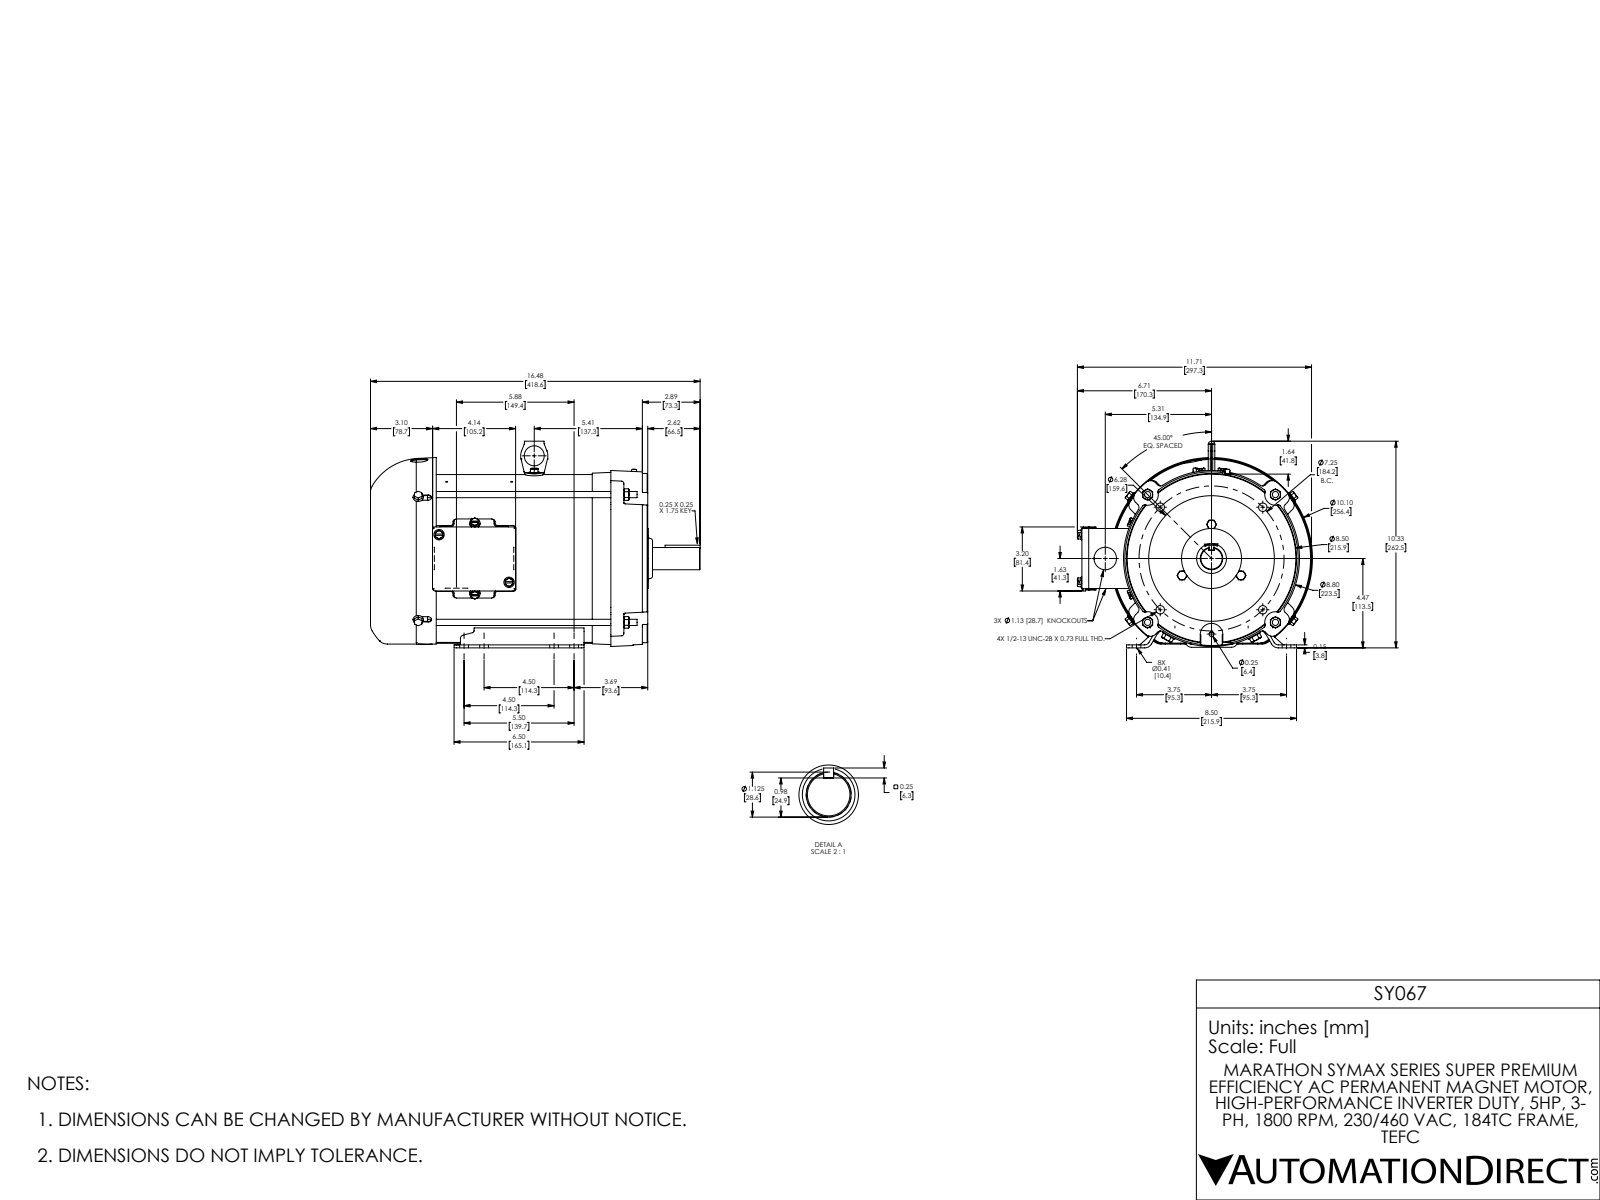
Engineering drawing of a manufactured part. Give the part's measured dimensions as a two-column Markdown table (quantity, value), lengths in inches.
| quantity | value |
| --- | --- |
| part name | 036316-800_RevA_184TC_5HP Coord |
| STEP written by | SolidWorks 2017 (AUTOMOTIVE_DESIGN) |
| units | inches |
| bodies | 44 solids, 2571 faces (693 planar, 825 cylindrical, 1053 other) |
| overall size | 16.481 × 11.753 × 10.334 |
| volume | 155.7 in³ |
| surface area | 1 674 in² |
| round holes (diameter × count) | 0.38 × 8, 0.213 × 7, 0.276 × 6, 0.435 × 6, 0.104 × 4, 0.236 × 4, 0.257 × 4, 0.28 × 4, 0.344 × 4, 0.422 × 4, 0.281 × 3, 0.25 × 2 |
| round bosses / shafts (diameter × count) | 0.25 × 13, 0.676 × 6, 0.52 × 6, 0.313 × 6, 0.31 × 6, 0.522 × 4, 0.33 × 3, 0.309 × 2 |
| partial cylindrical surfaces (radius × count) | 0.125 × 64, 0.12 × 46, 0.13 × 20, 0.09 × 16, 0.19 × 16, 0.03 × 8, 0.165 × 8, 0.25 × 8 |
| main face-to-face distances | 0.048, 0.2, 0.15, 11.47, 11.27, 11.69, 11.49, 0.22, 12.115, 11.915 |
| hole center spacings | 5.793, 2.31, 0.893, 1, 2.315, 3.5, 3.625, 4.5 |
